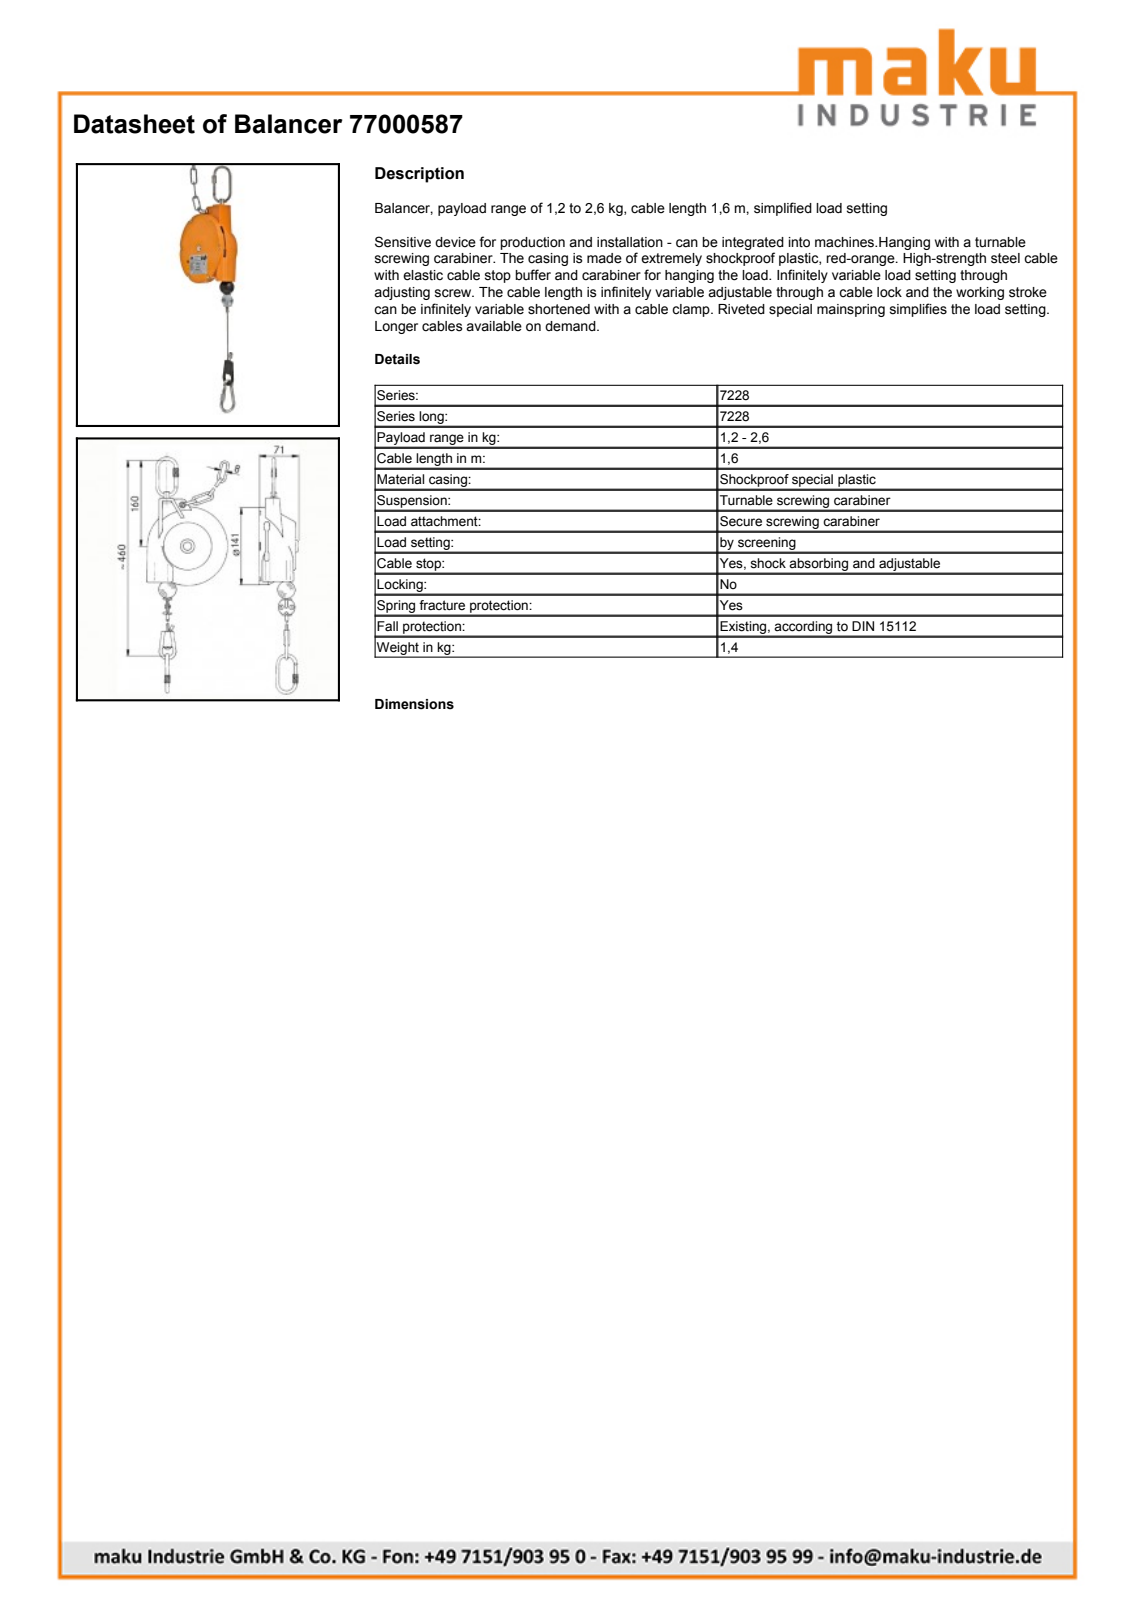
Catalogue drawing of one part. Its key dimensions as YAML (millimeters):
part_name: "002-7228000001-Ab"
step_written_by: "Autodesk Inventor 2014 (CONFIG_CONTROL_DESIGN)"
units: millimeters
bodies: {solids: 14, faces: 979, planar: 452, cylindrical: 242, other: 285}
overall_size: [637.12, 153.88, 77.1]
volume: 883925
surface_area: 94544
round_holes:
  - {diameter: 4.3, count: 2}
  - {diameter: 1.7, count: 1}
  - {diameter: 2.1, count: 1}
  - {diameter: 2.5, count: 1}
  - {diameter: 3, count: 1}
  - {diameter: 4, count: 1}
  - {diameter: 5.5, count: 1}
  - {diameter: 6, count: 1}
  - {diameter: 6.6, count: 1}
  - {diameter: 6.8, count: 1}
  - {diameter: 7, count: 1}
  - {diameter: 7.5, count: 1}
round_bosses_or_shafts:
  - {diameter: 4, count: 7}
  - {diameter: 6.8, count: 4}
  - {diameter: 6, count: 3}
  - {diameter: 5, count: 3}
  - {diameter: 10, count: 2}
  - {diameter: 8, count: 2}
  - {diameter: 3.62, count: 2}
  - {diameter: 141, count: 1}
partial_cylinders:
  - {radius: 0.13, count: 32}
  - {radius: 0.5, count: 9}
  - {radius: 1.5, count: 9}
  - {radius: 1, count: 6}
  - {radius: 0.8, count: 5}
  - {radius: 3.5, count: 4}
  - {radius: 4, count: 4}
  - {radius: 5, count: 4}
face_to_face_distances: [67.5, 67.6, 1.5, 0.5, 5, 2.5, 2, 6, 51, 4.5]
hole_center_spacings: [17, 11.32, 11.42, 23.3, 28.71, 45.53, 45.54, 46.46]
